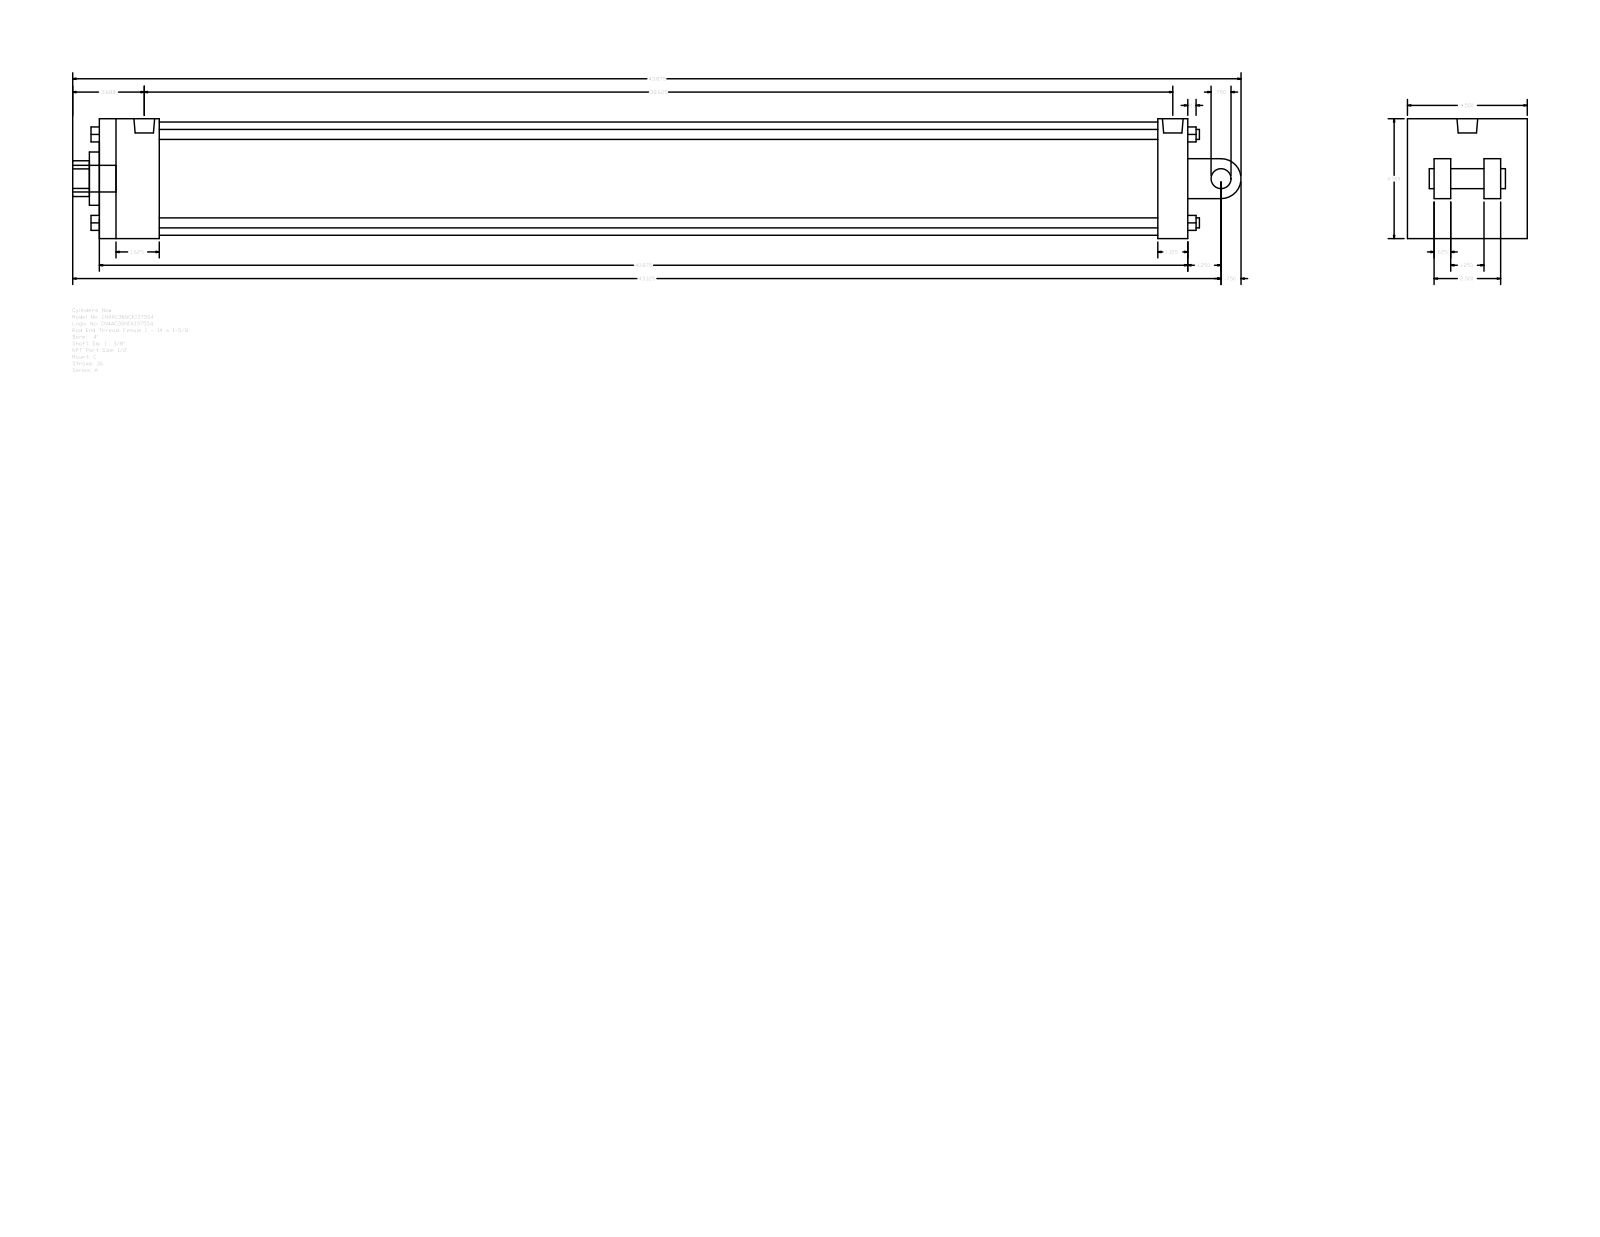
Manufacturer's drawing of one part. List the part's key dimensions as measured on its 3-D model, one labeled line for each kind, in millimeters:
Part name (STEP PRODUCT): A_C__0400_1.375
STEP written by: GSSL Pune (CONFIG_CONTROL_DESIGN)
Units: millimetres
Bodies: 0 solids, 135 faces (102 planar, 33 cylindrical, 0 other)
Overall size (bounding box): 1114.42 × 114.3 × 114.3
Round holes (diameter × count): ⌀8.73 ×2, ⌀19.77 ×1, ⌀34.92 ×1, ⌀50.8 ×1, ⌀107.95 ×1
Round bosses / shafts (diameter × count): ⌀9.53 ×4, ⌀8.73 ×2, ⌀25.4 ×1, ⌀19.77 ×1, ⌀19.05 ×1
Partial cylindrical surfaces — rounded edges, fillets, slot ends (radius × count): R17.06 ×1, R19.05 ×1
Main face-to-face distances: 114.3, 1038.22, 73.03, 28.57, 1009.65, 57.15, 952.5, 981.07, 15.87, 41.27
Hole centre spacings: 3.18
